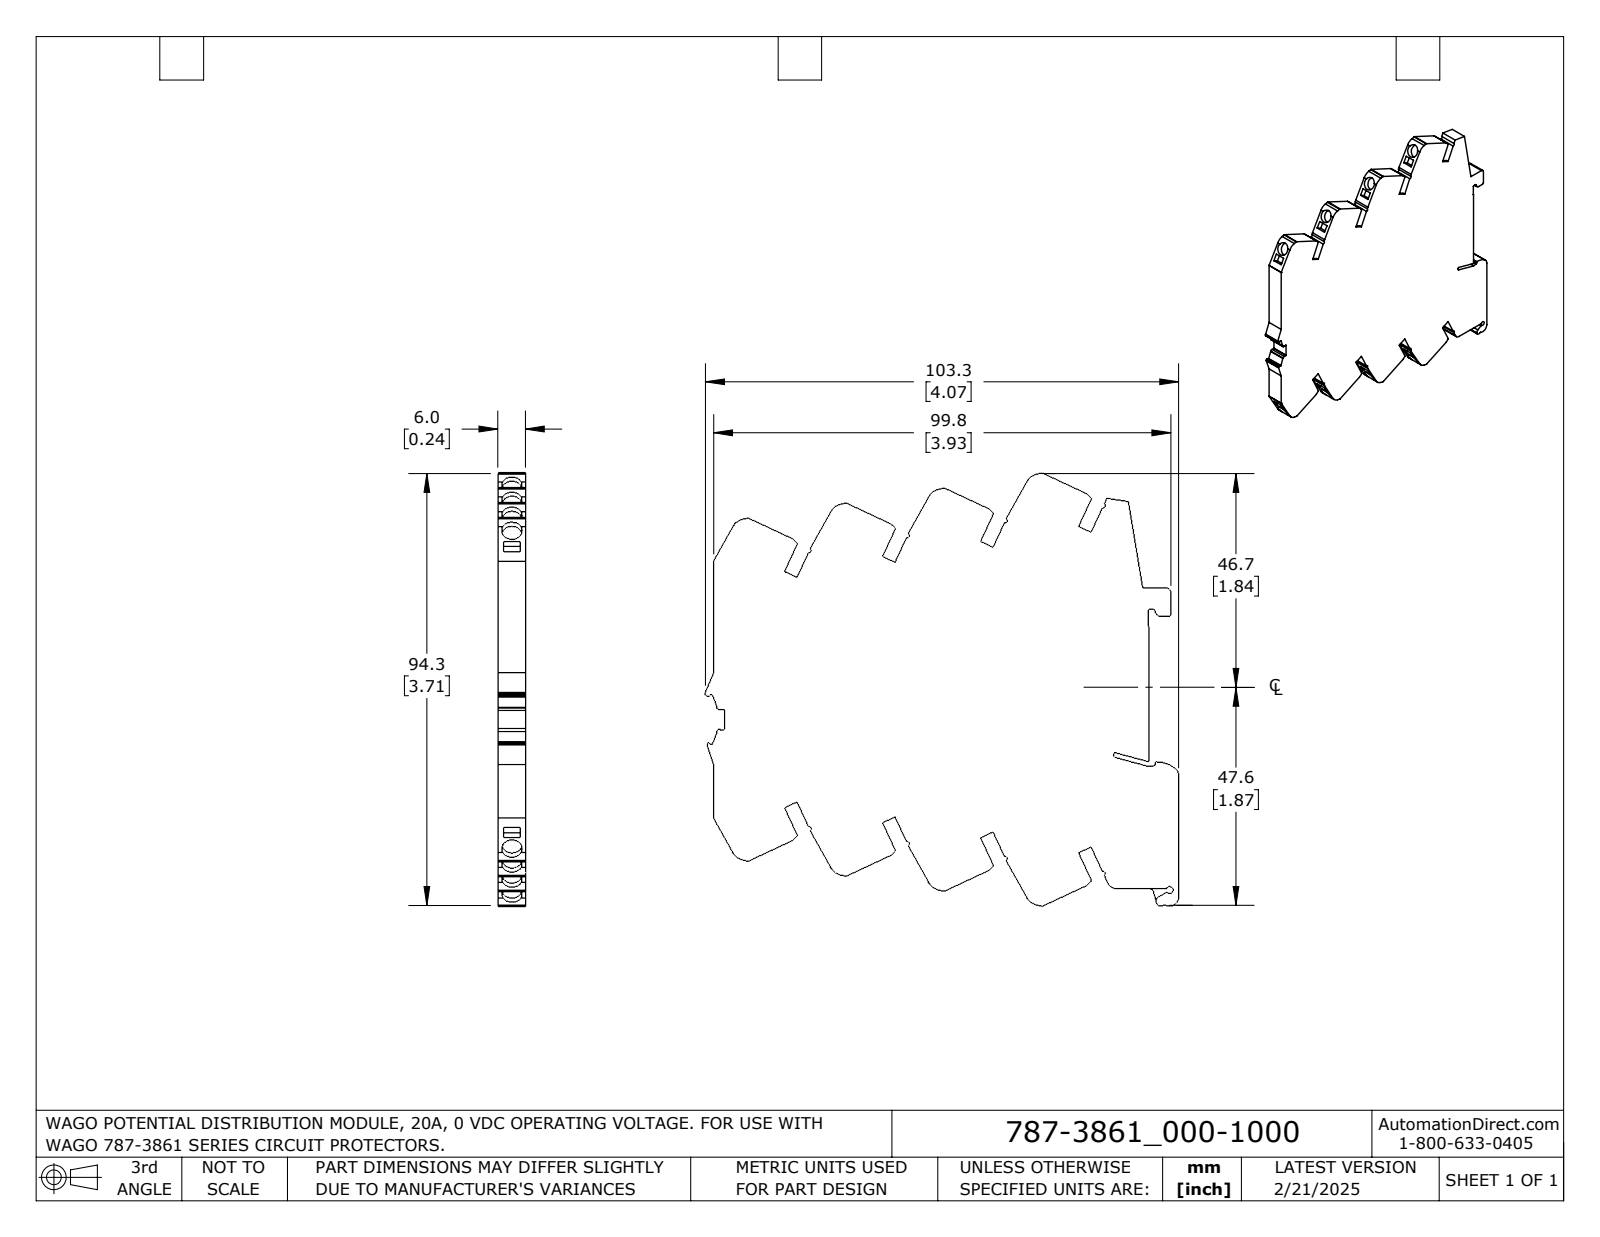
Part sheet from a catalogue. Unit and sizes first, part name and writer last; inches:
Units: inches
Overall size (bounding box): 4.067 × 3.711 × 0.236
Round holes (diameter × count): ⌀0.173 ×8
Partial cylindrical surfaces — rounded edges, fillets, slot ends (radius × count): R0.008 ×13, R0.02 ×12, R0.016 ×8, R0.132 ×8, R0.039 ×5, R0.012 ×3, R0.079 ×3, R0.018 ×2
Main face-to-face distances: 0.236, 0.708, 0.67, 0.473, 0.472, 1.34, 1.417, 0.118, 1.417, 0.079
Hole centre spacings: 0.526, 0.525, 1.051, 1.052, 1.577
Volume: 2.685 in³ · Surface area: 29.22 in²
Bodies: 1 solid, 255 faces (191 planar, 64 cylindrical, 0 other)
Part name (STEP PRODUCT): 787-3861_000-1000_HI
STEP written by: SolidWorks 2024 (AUTOMOTIVE_DESIGN)
